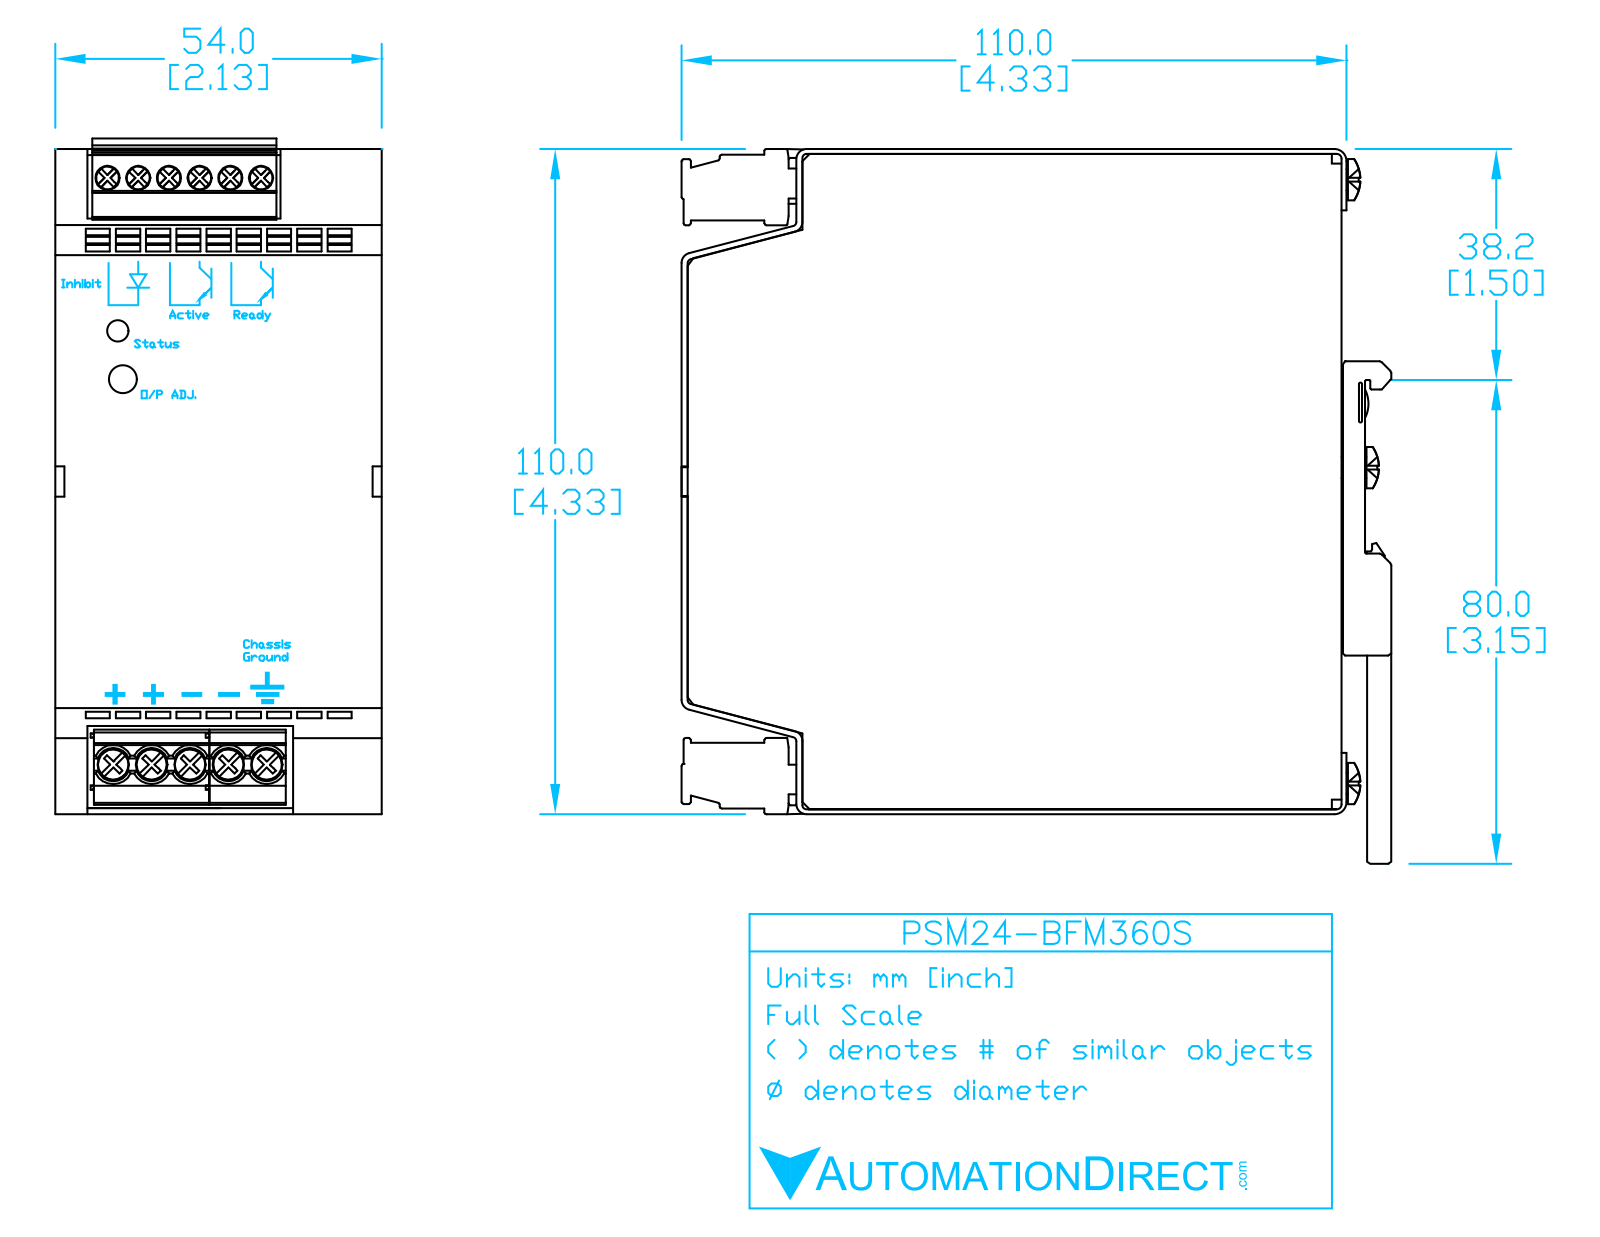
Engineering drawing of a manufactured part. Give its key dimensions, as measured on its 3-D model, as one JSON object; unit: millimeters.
{"part_name": "PSM24-BFM600S", "step_written_by": "SolidWorks 2011 (CONFIG_CONTROL_DESIGN)", "units": "millimeters", "bodies": {"solids": 1, "faces": 2353, "planar": 2192, "cylindrical": 72, "other": 89}, "overall_size": [119.2, 119.2, 54.1], "volume_mm3": 632500, "surface_area_mm2": 61550, "round_holes": [[4.1, 10], [3.8, 1], [4.4, 1]], "round_bosses_or_shafts": [[5.3, 2], [6.7, 1], [2.8, 1], [1, 1], [1, 1]], "partial_cylinders_radius": [[1.5, 16], [0.5, 4], [0.8, 2], [1.8, 2], [2.1, 2]], "face_to_face_distances": [54.1, 1, 109, 110, 109, 108, 1, 14.5, 39.5, 109], "hole_center_spacings": [5.1, 10.2, 15.2, 20.3, 7.9, 25.4, 33, 98.6]}
